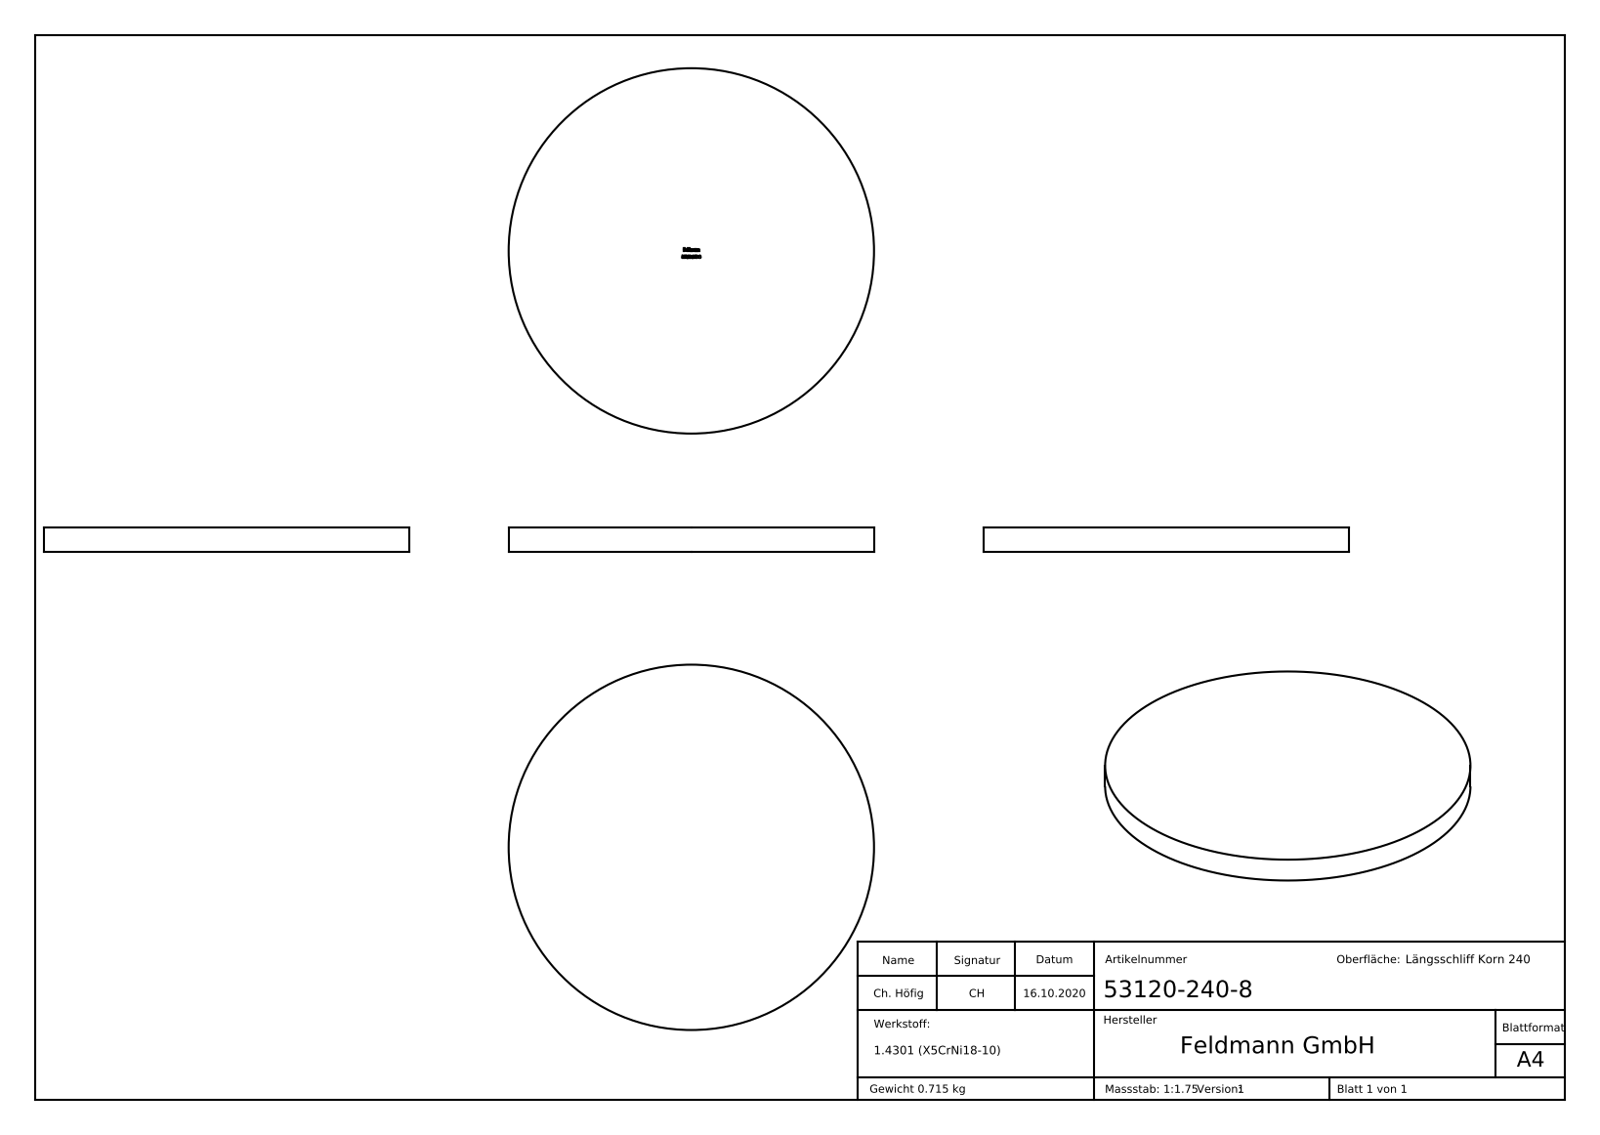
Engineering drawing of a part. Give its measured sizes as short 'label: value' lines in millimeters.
name: 53120-240-8
written by: SolidWorks 2018 (CONFIG_CONTROL_DESIGN)
unit: mm
bodies: 1 solid, 250 faces (131 planar, 2 cylindrical, 117 other)
size: 120 × 120 × 8
volume: 90 478 mm³; area: 25 642 mm²
bosses: 1× ⌀120
face distances: 8, 7.9, 0.83, 1.78, 2.61, 0.76, 1.02, 2.45, 0.95, 3.03
